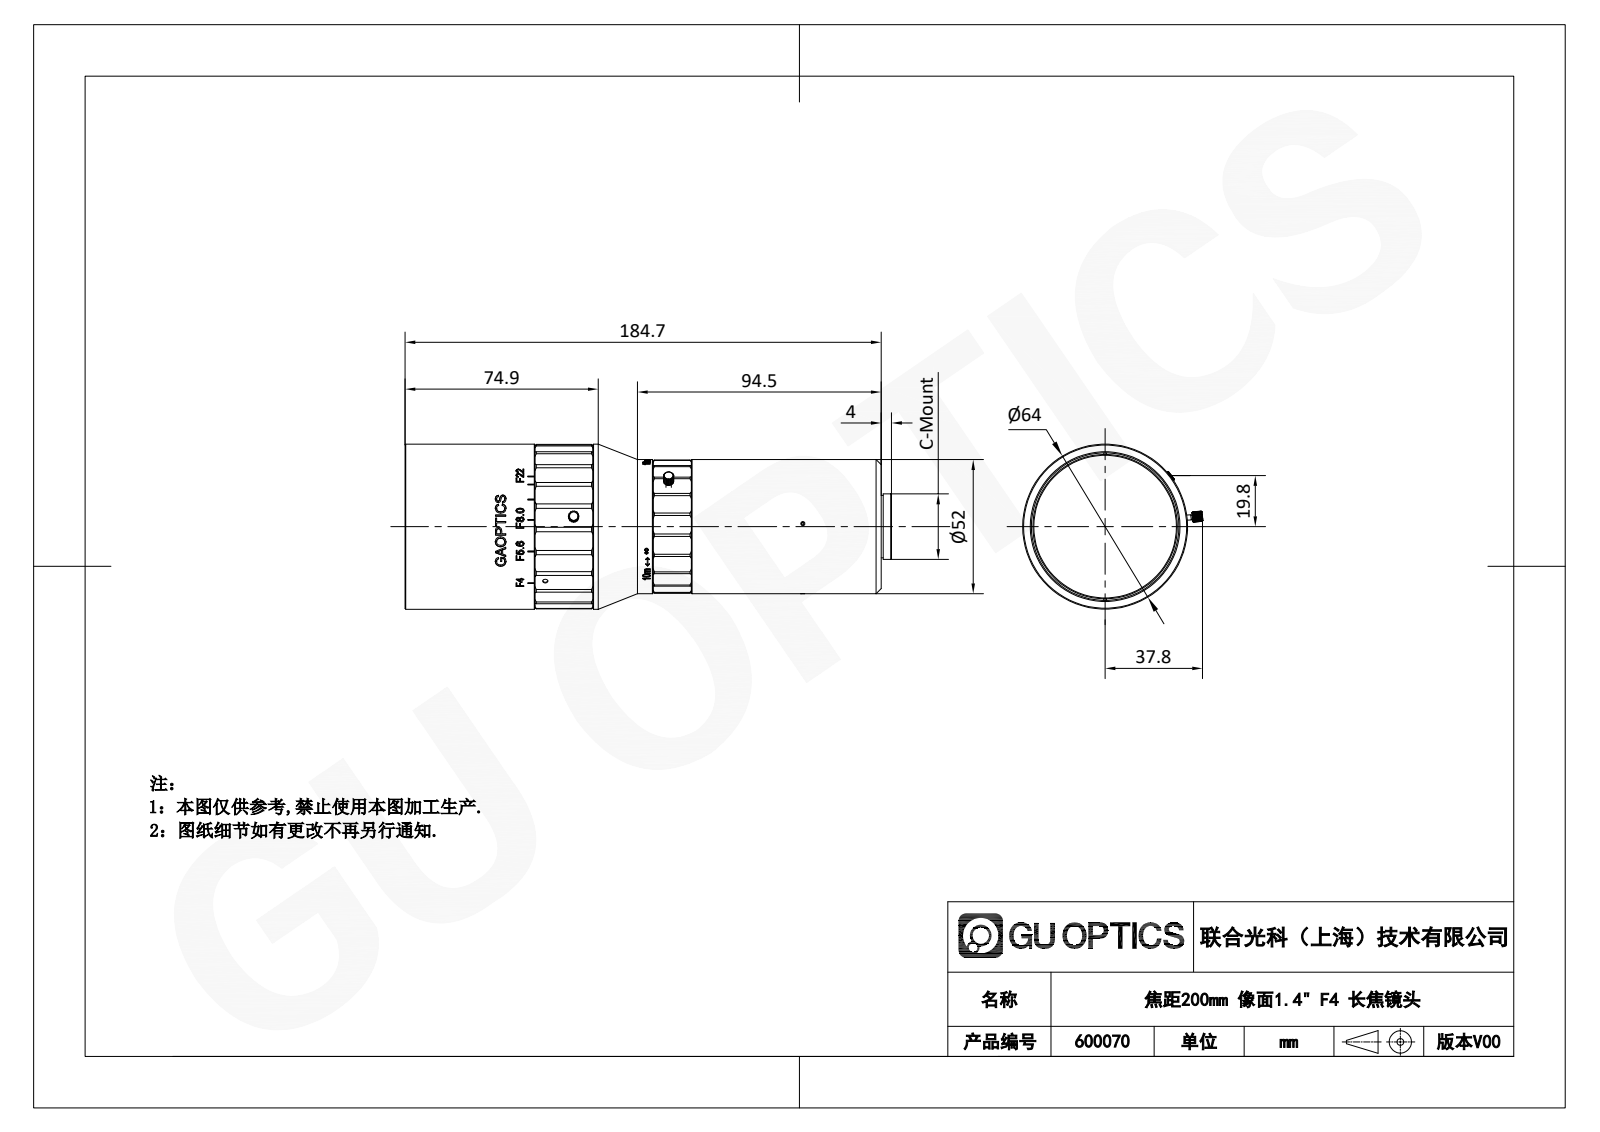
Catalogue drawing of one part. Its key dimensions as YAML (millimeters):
part_name: "600070; 600070-SC2; 600070-R2; 600070 REAR ASSEMBLE (+8 more)"
step_written_by: "SolidWorks 2025 (AUTOMOTIVE_DESIGN)"
units: millimeters
bodies: {solids: 35, faces: 1627, planar: 552, cylindrical: 539, other: 536}
overall_size: [188.66, 69.96, 64]
volume: 231618
surface_area: 158116
round_holes:
  - {diameter: 1.6, count: 12}
  - {diameter: 2, count: 5}
  - {diameter: 1.2, count: 4}
  - {diameter: 1.8, count: 4}
  - {diameter: 2.1, count: 3}
  - {diameter: 22, count: 1}
  - {diameter: 24.8, count: 1}
  - {diameter: 27, count: 1}
  - {diameter: 28.4, count: 1}
  - {diameter: 29.2, count: 1}
  - {diameter: 30, count: 1}
  - {diameter: 31.4, count: 1}
round_bosses_or_shafts:
  - {diameter: 2, count: 11}
  - {diameter: 3, count: 5}
  - {diameter: 1.6, count: 4}
  - {diameter: 1.05, count: 4}
  - {diameter: 3.8, count: 3}
  - {diameter: 1.5, count: 2}
  - {diameter: 64, count: 1}
  - {diameter: 61.3, count: 1}
partial_cylinders:
  - {radius: 9, count: 42}
  - {radius: 0.1, count: 30}
  - {radius: 1.5, count: 6}
  - {radius: 2, count: 2}
  - {radius: 25.98, count: 1}
  - {radius: 27.1, count: 1}
  - {radius: 31.98, count: 1}
face_to_face_distances: [129.72, 84.55, 101.55, 28.17, 17, 112.72, 1.1, 15.9, 100.45, 128.62]
hole_center_spacings: [3.64]
